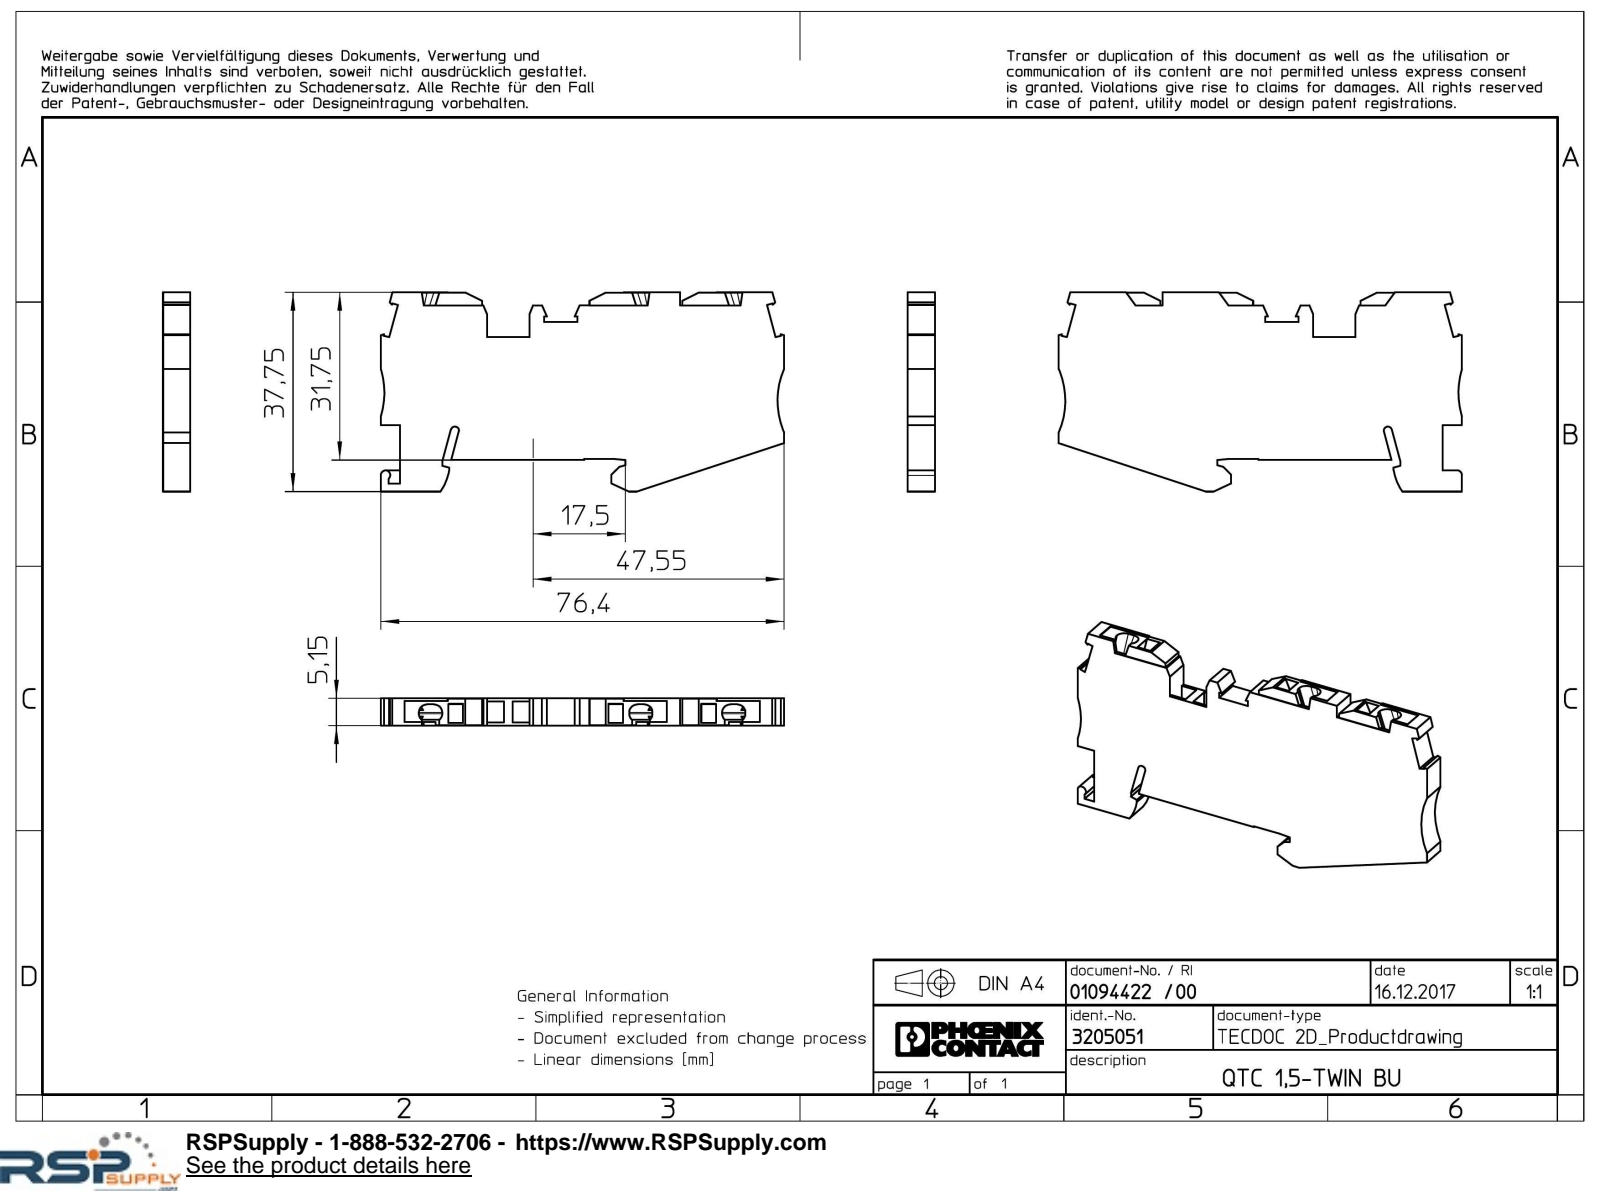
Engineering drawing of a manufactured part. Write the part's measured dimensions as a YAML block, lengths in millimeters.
part_name: "QTC_1.5-TWIN_BU-select"
step_written_by: "Creo Elements/Direct Modeling 20.1A 29-Sep-2018 (C) Parametric Technology GmbH (AUTOMOTIVE_DESIGN)"
units: millimeters
bodies: {solids: 1, faces: 170, planar: 152, cylindrical: 18, other: 0}
overall_size: [76.4, 37.75, 5.15]
volume: 11063
surface_area: 7299
partial_cylinders:
  - {radius: 1.5, count: 12}
  - {radius: 15, count: 2}
  - {radius: 0.7, count: 1}
  - {radius: 0.8, count: 1}
  - {radius: 0.9, count: 1}
  - {radius: 9.5, count: 1}
face_to_face_distances: [5.15, 4, 3.6, 0.47, 0.57, 3.15, 4.85, 0.5, 1.21, 2.39]
